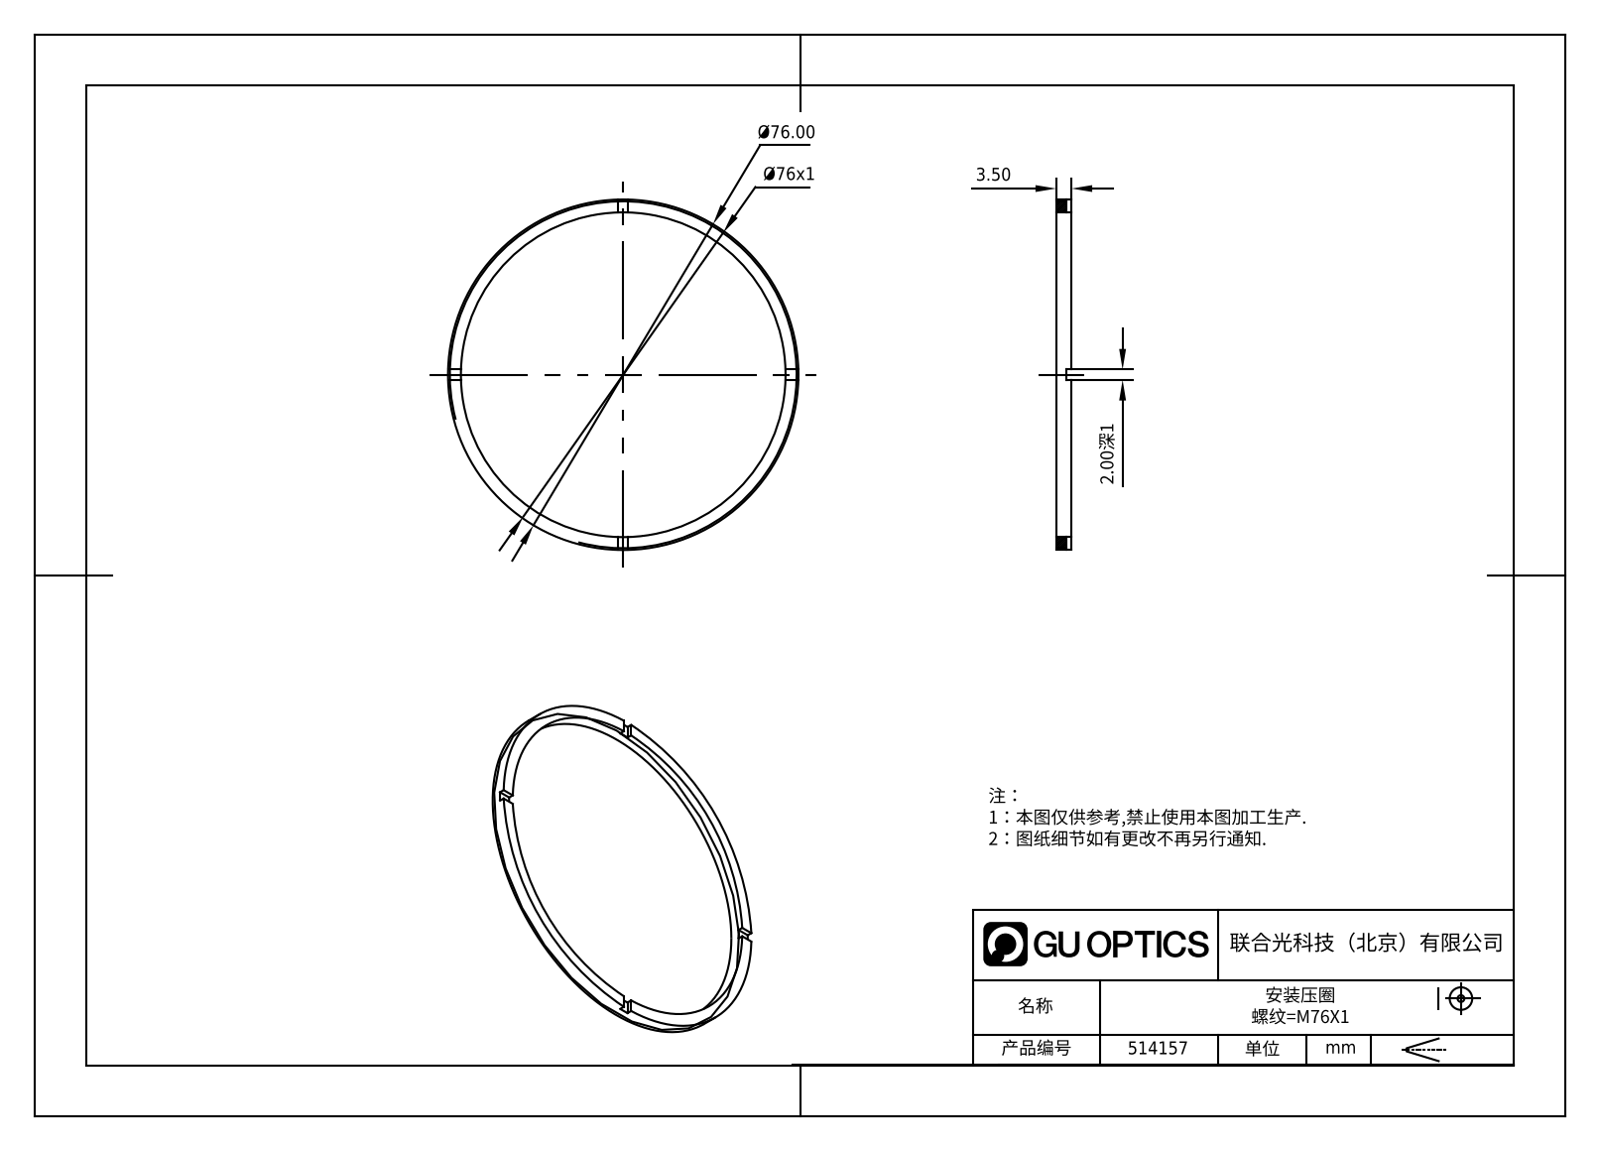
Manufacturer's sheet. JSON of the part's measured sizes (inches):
{"part_name": "514157", "step_written_by": "SolidWorks 2020 (CONFIG_CONTROL_DESIGN)", "units": "inches", "bodies": {"solids": 1, "faces": 21, "planar": 17, "cylindrical": 4, "other": 0}, "overall_size": [2.992, 2.992, 0.138], "volume_in3": 0.145, "surface_area_in2": 4.633, "round_holes": [[2.756, 1]], "round_bosses_or_shafts": [[2.992, 1]], "face_to_face_distances": [0.138, 0.098, 0.039, 0.079]}
